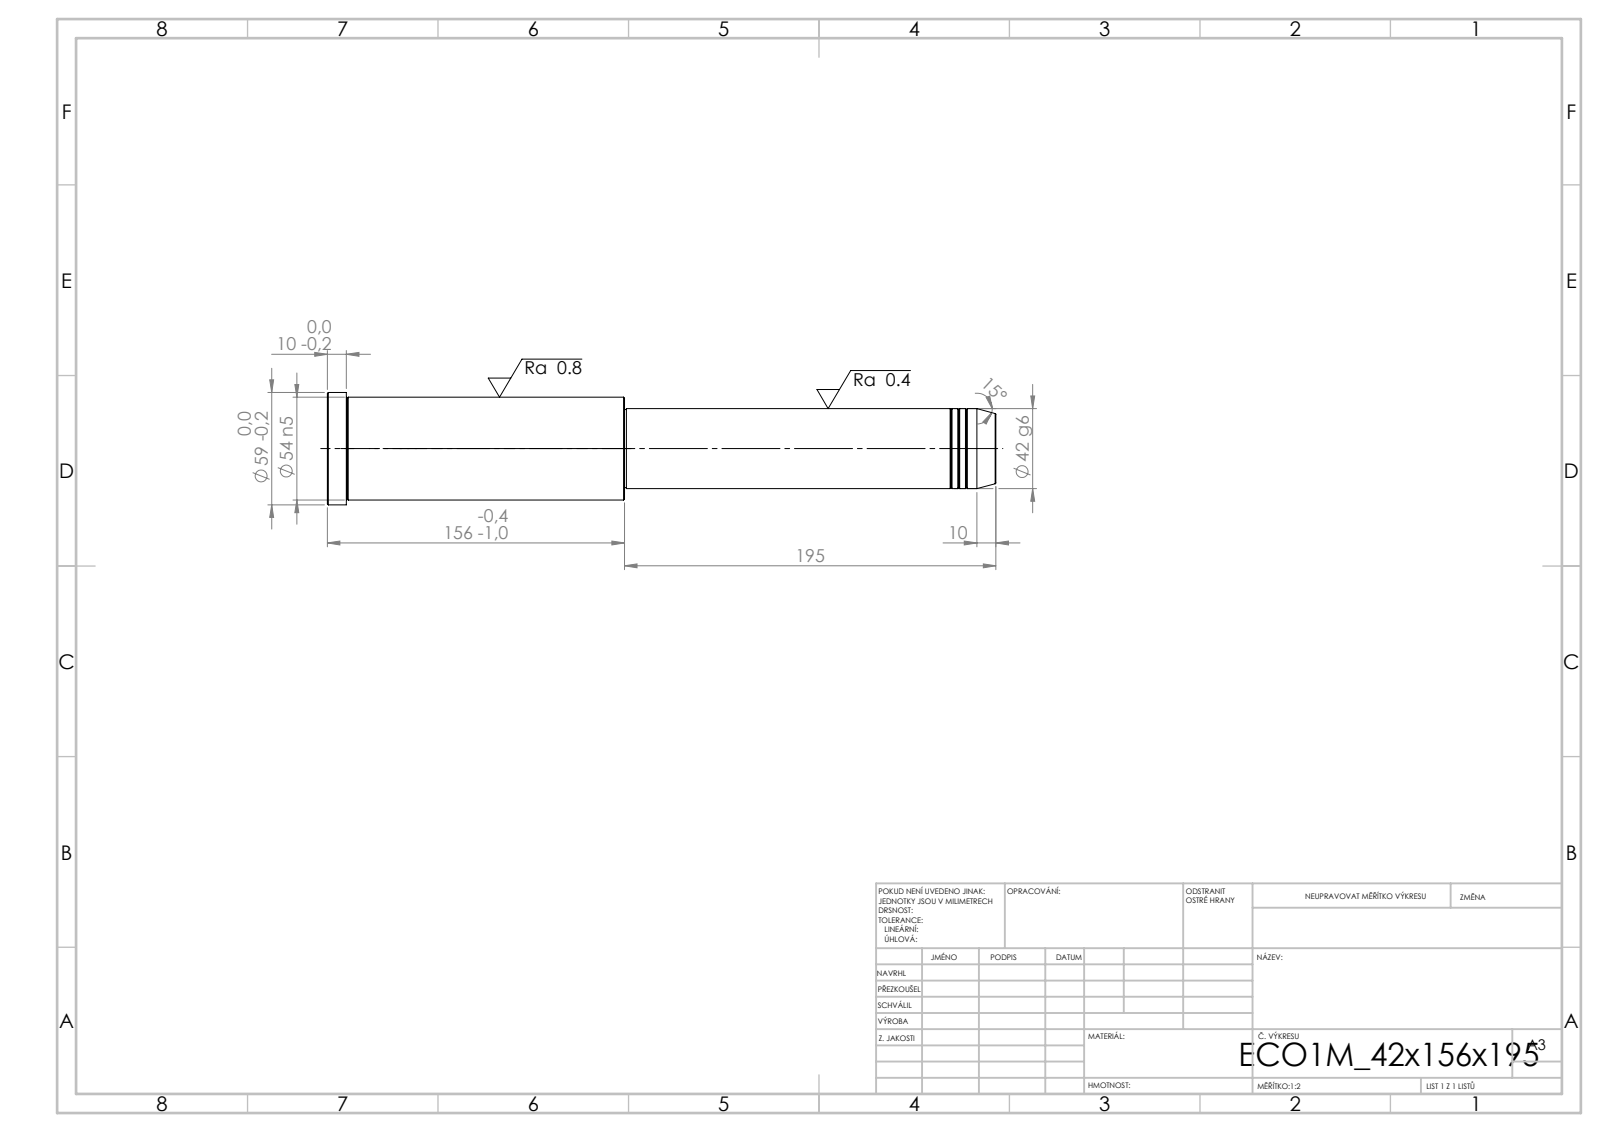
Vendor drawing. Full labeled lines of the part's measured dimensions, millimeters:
STEP written by: SolidWorks 2019 (CONFIG_CONTROL_DESIGN)
Units: millimetres
Bodies: 1 solid, 43 faces (5 planar, 14 cylindrical, 24 other)
Overall size (bounding box): 351 × 59 × 59
Volume: 629 848 mm³ · Surface area: 57 768 mm²
Round bosses / shafts (diameter × count): ⌀59 ×1, ⌀54 ×1, ⌀42 ×1, ⌀41 ×1
Main face-to-face distances: 351, 195, 156, 341, 146, 10, 194, 1, 147, 157
